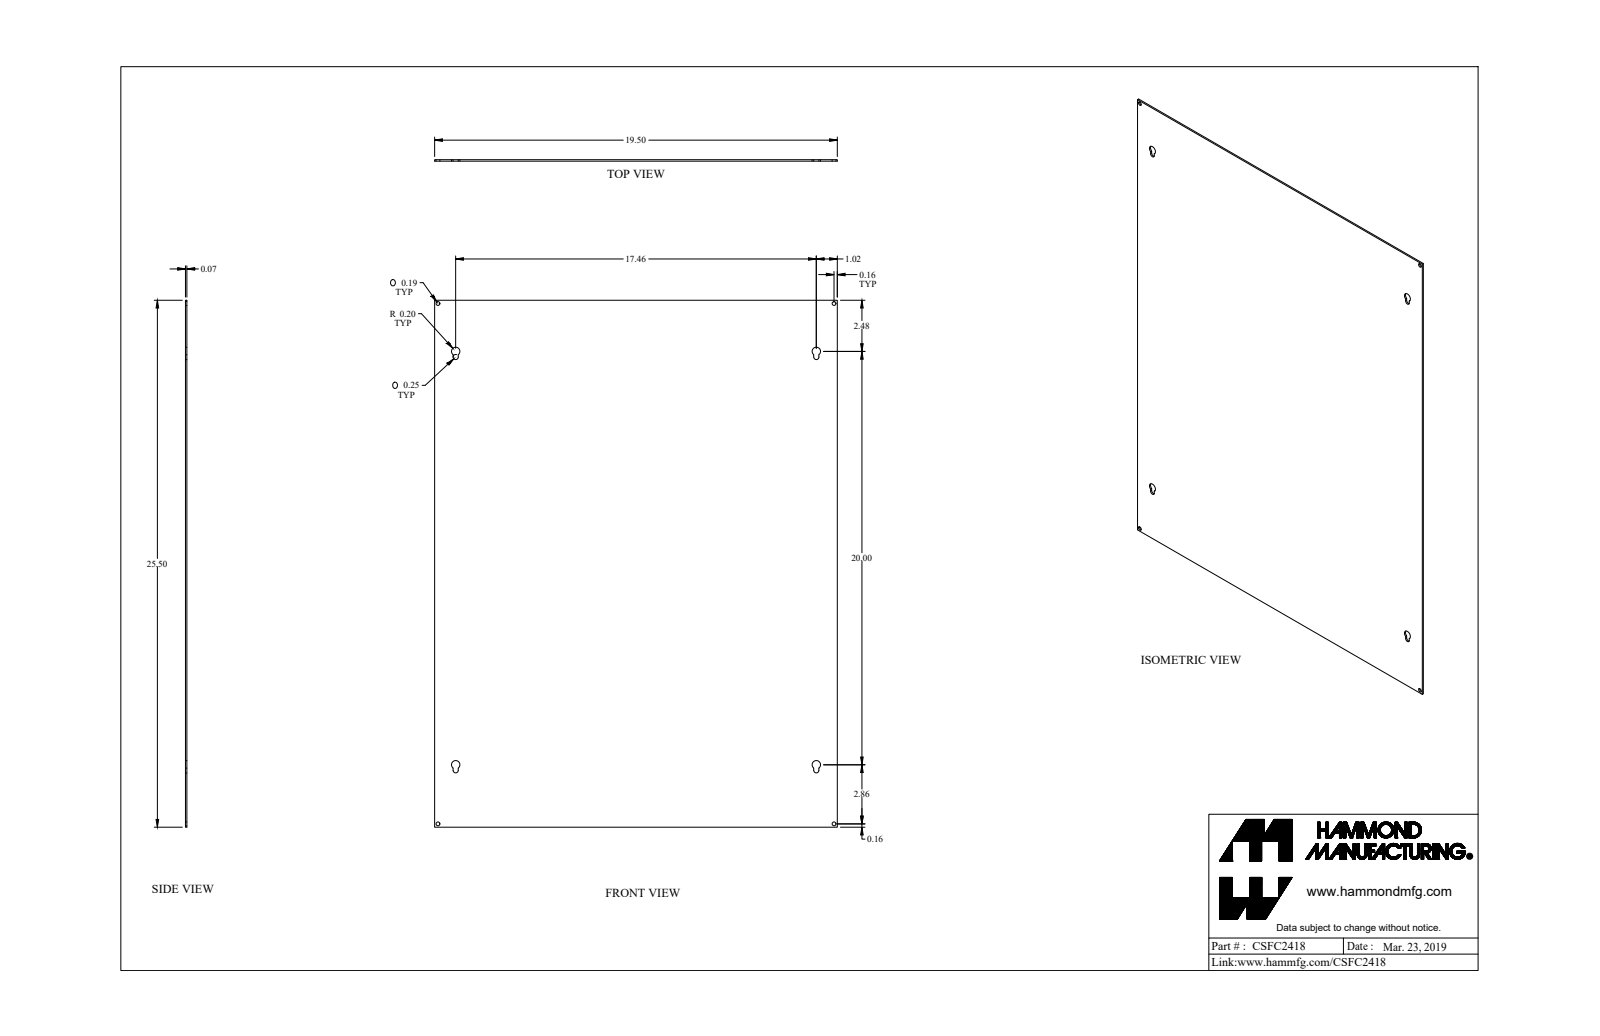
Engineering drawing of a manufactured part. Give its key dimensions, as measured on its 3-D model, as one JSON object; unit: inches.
{"part_name": "CSFC2418_Default", "step_written_by": "SolidWorks 2019 (CONFIG_CONTROL_DESIGN)", "units": "inches", "bodies": {"solids": 1, "faces": 38, "planar": 14, "cylindrical": 24, "other": 0}, "overall_size": [25.5, 19.5, 0.072], "volume_in3": 35.74, "surface_area_in2": 1000, "round_holes": [[0.188, 4]], "partial_cylinders_radius": [[0.125, 4], [0.203, 4]], "face_to_face_distances": [0.072, 19.5, 25.5, 0.895, 18.605, 1.145, 18.355, 17.46, 0.25, 17.71], "hole_center_spacings": [19.18, 25.18, 31.653]}
